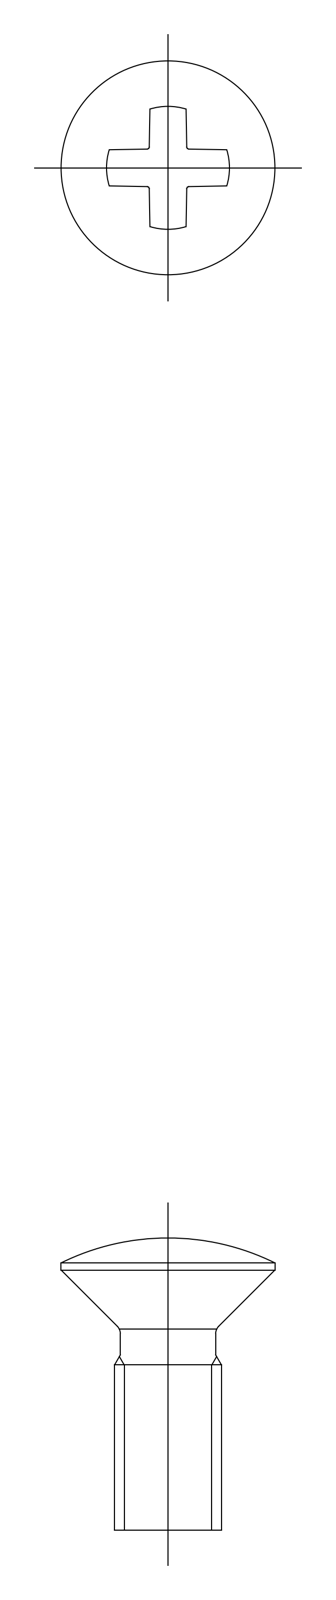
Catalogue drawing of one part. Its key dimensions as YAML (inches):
part_name: "screw"
step_written_by: "CADfix (AUTOMOTIVE_DESIGN)"
units: inches
bodies: {solids: 1, faces: 27, planar: 0, cylindrical: 0, other: 27}
overall_size: [0.643, 0.472, 0.472]
volume: 0.037
surface_area: 0.822
